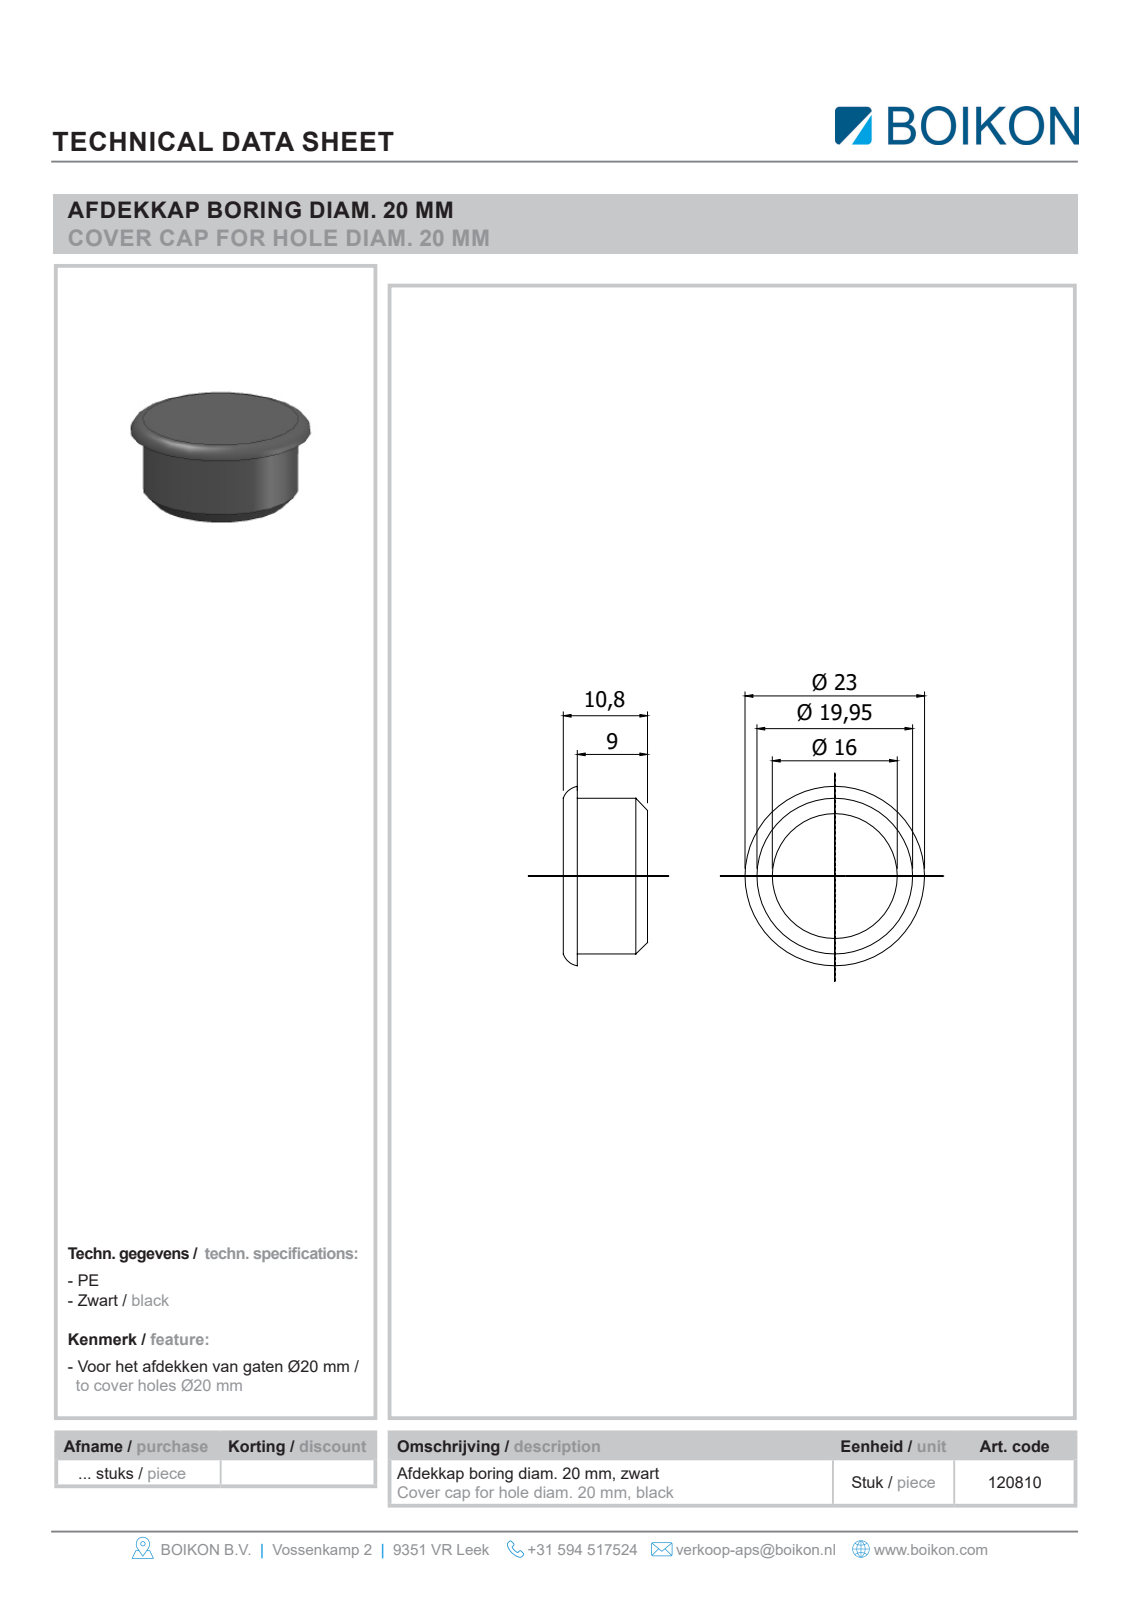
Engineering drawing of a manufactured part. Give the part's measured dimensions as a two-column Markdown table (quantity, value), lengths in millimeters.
| quantity | value |
| --- | --- |
| part name | Root; 120810Afdekkap boring diam 20 mm zwartBOIKON |
| STEP written by | HiCAD 2013 1802.4 Build 509 (AUTOMOTIVE_DESIGN) |
| units | millimeters |
| bodies | 1 solid, 8 faces (4 planar, 2 cylindrical, 2 other) |
| overall size | 23.2 × 23.2 × 11 |
| volume | 1 625 mm³ |
| surface area | 1 912 mm² |
| round holes (diameter × count) | 16 × 1 |
| round bosses / shafts (diameter × count) | 20 × 1 |
| main face-to-face distances | 1.6, 9.4, 11 |
